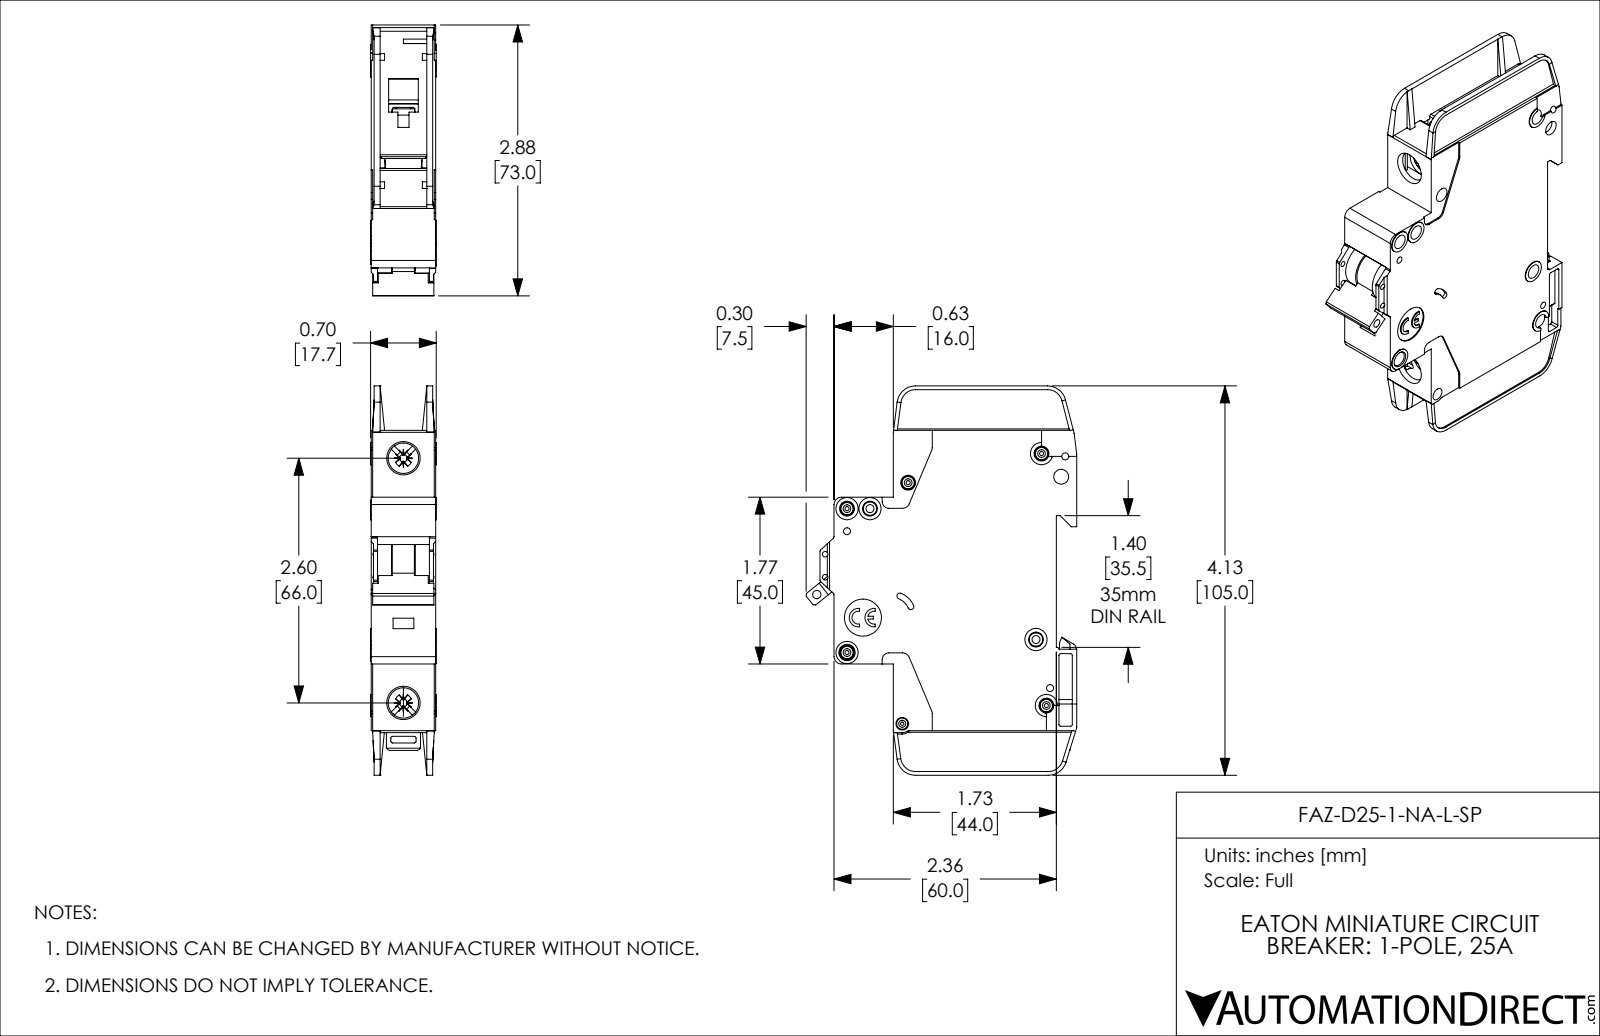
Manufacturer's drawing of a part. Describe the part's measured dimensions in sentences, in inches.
The part is named "FAZ-D25-1-NA-L-SP". Its 3-D file was written by "SolidWorks 2019 (AUTOMOTIVE_DESIGN)". It is 1 solid with 1127 faces: 671 planar, 357 cylindrical and 99 other. Overall it measures 4.134 by 2.876 by 0.697 inches. Its volume is 4.682 cubic inches and its surface area 41.01 square inches. Round holes: 8 of diameter 0.157, 5 of diameter 0.043, 4 of diameter 0.075, 2 of diameter 0.059, 2 of diameter 0.085, 2 of diameter 0.323, 1 of diameter 0.035, 1 of diameter 0.089, 1 of diameter 0.098, 1 of diameter 0.134, 1 of diameter 0.394. Round bosses or shafts: 5 of diameter 0.13, 4 of diameter 0.236, 2 of diameter 0.118, 1 of diameter 0.098. Partial cylindrical surfaces (rounded edges, fillets, slot ends): 42 of radius 0.02, 10 of radius 0.016, 10 of radius 0.039, 8 of radius 0.079, 5 of radius 0.197, 4 of radius 0.008, 4 of radius 0.026, 4 of radius 0.043. The main face-to-face distances are 0.047, 0.685, 0.591, 0.638, 0.094, 0.543, 0.016, 0.031, 0.496, 0.575. The hole center spacings are 0.244, 0.537, 0.87, 0.189, 0.199, 0.204, 0.221, 0.24.
